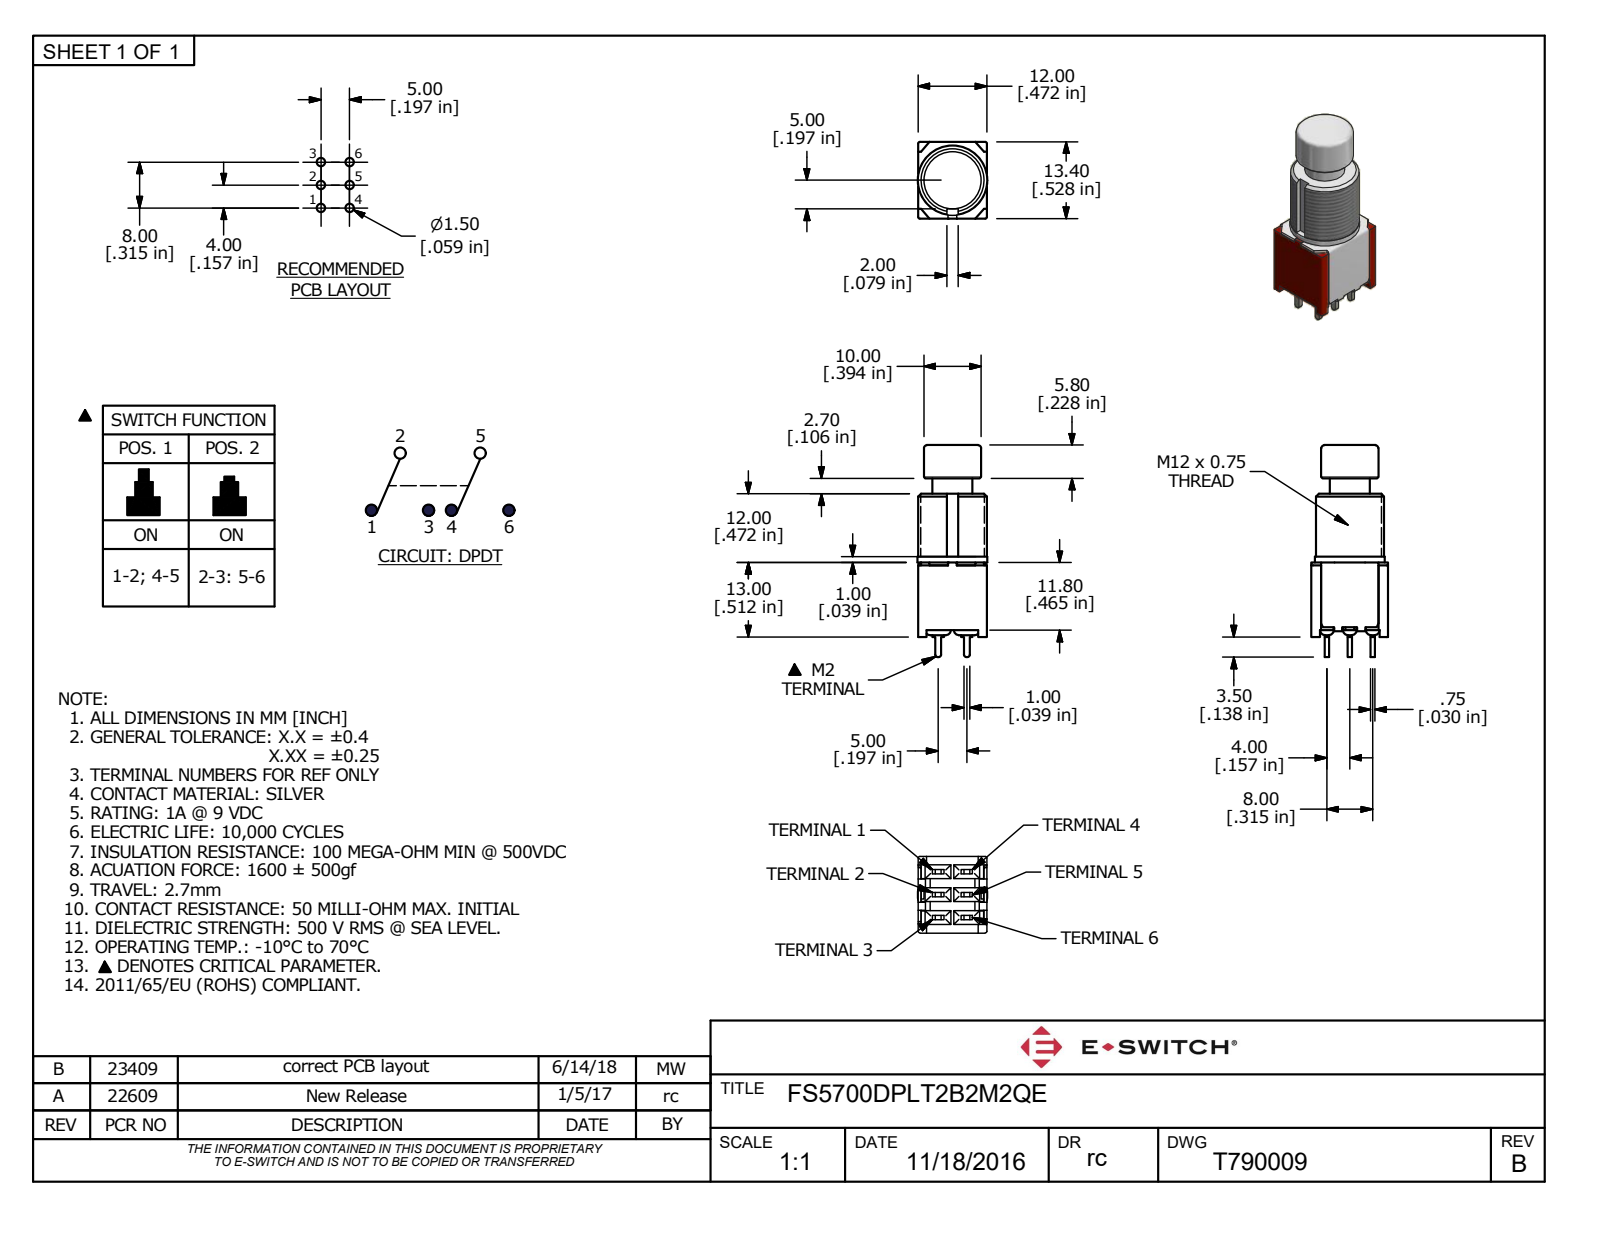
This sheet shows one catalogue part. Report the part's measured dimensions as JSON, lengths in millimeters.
{"part_name": "FS5700DPLT2B2M2QE", "step_written_by": "Autodesk Inventor 2022 (AUTOMOTIVE_DESIGN)", "units": "millimeters", "bodies": {"solids": 1, "faces": 338, "planar": 252, "cylindrical": 83, "other": 3}, "overall_size": [37, 13.4, 12.2], "volume_mm3": 2131, "surface_area_mm2": 3332, "round_holes": [[9, 1]], "round_bosses_or_shafts": [[12.2, 1], [12, 1], [10, 1], [7, 1]], "partial_cylinders_radius": [[0.2, 26], [0.9, 10], [0.3, 4], [0.4, 4], [0.5, 4], [0.1, 2]], "face_to_face_distances": [1.2, 0.5, 11, 10.8, 0.7, 10.3, 11.5, 12, 0.55, 11.45]}
